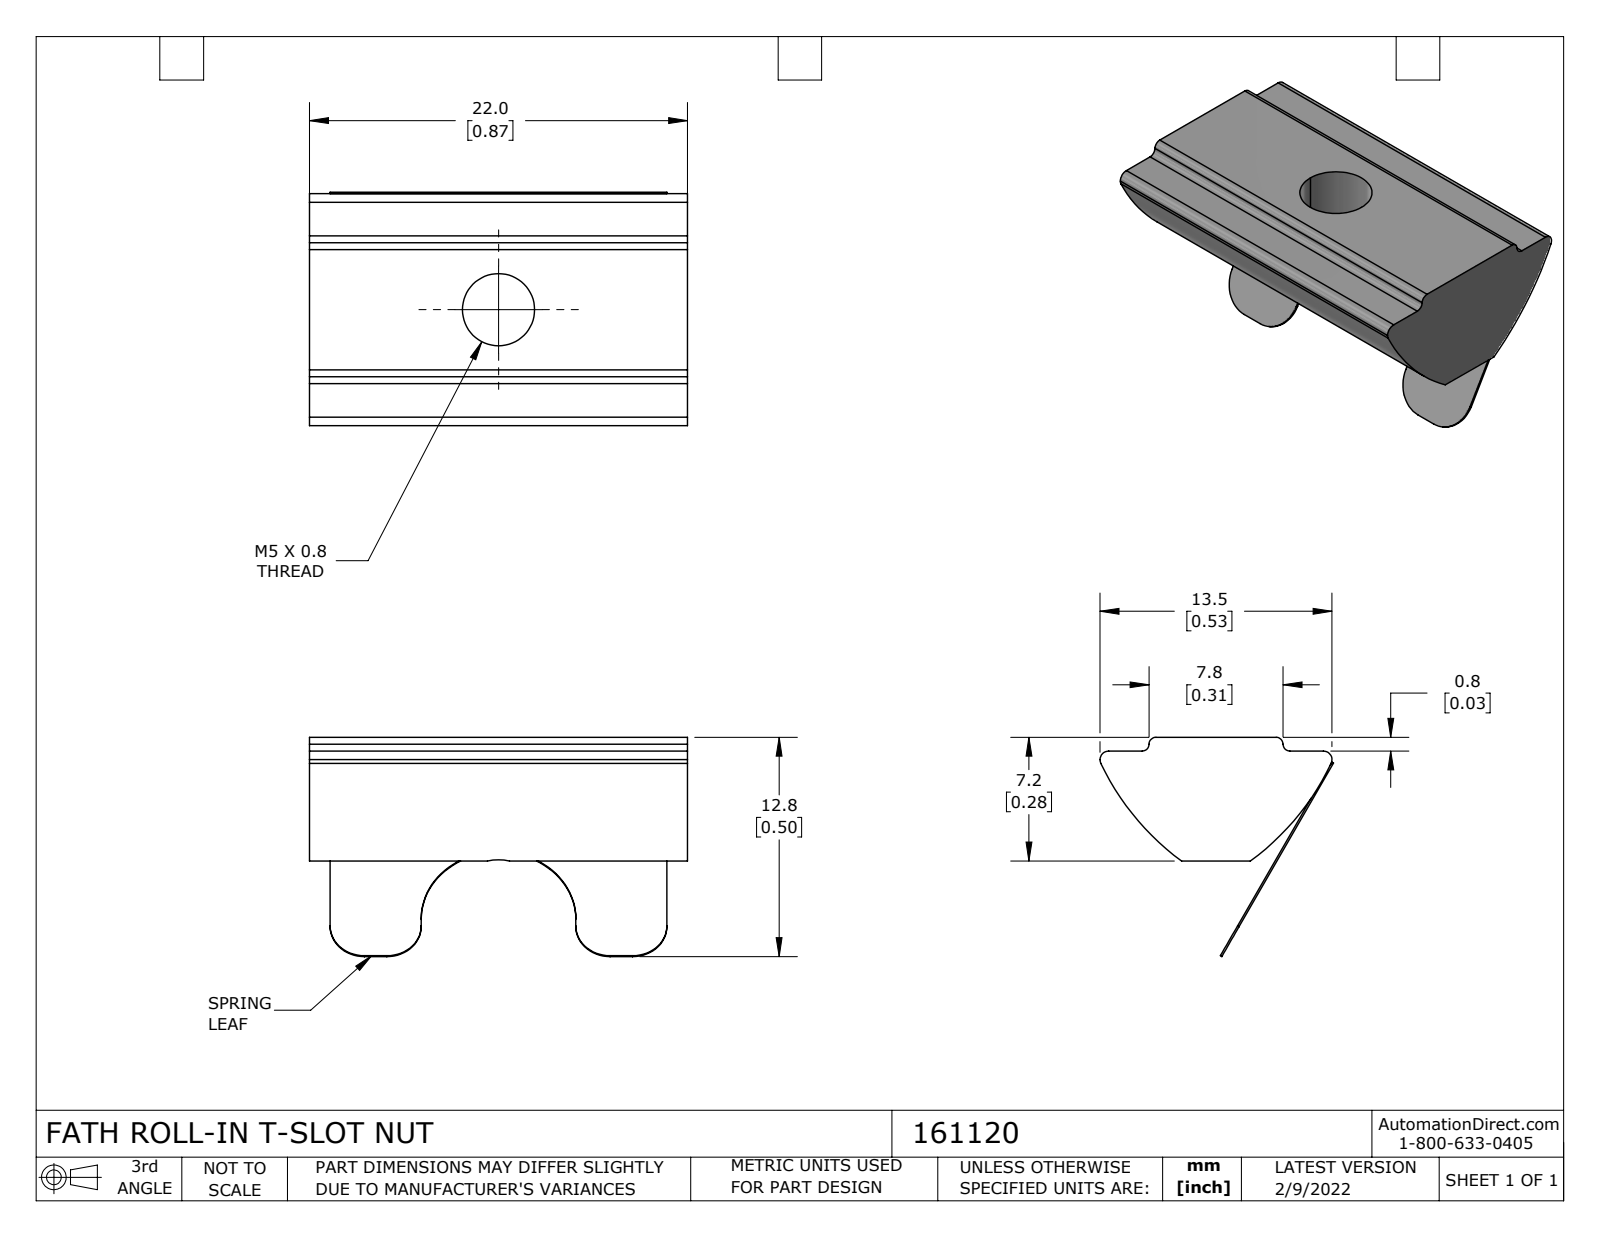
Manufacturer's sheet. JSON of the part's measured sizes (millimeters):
{"part_name": "161120", "step_written_by": "SolidWorks 2021 (CONFIG_CONTROL_DESIGN)", "units": "millimeters", "bodies": {"solids": 1, "faces": 33, "planar": 17, "cylindrical": 16, "other": 0}, "overall_size": [22, 13.59, 12.76], "volume_mm3": 1454, "surface_area_mm2": 1278, "round_holes": [[4.2, 1]], "partial_cylinders_radius": [[0.4, 4], [2, 4], [0.5, 2], [15, 2], [4.5, 1]], "face_to_face_distances": [0.8, 6.4, 7.2, 22, 1.2, 20.8, 19.6, 13, 6.5, 15.5]}
